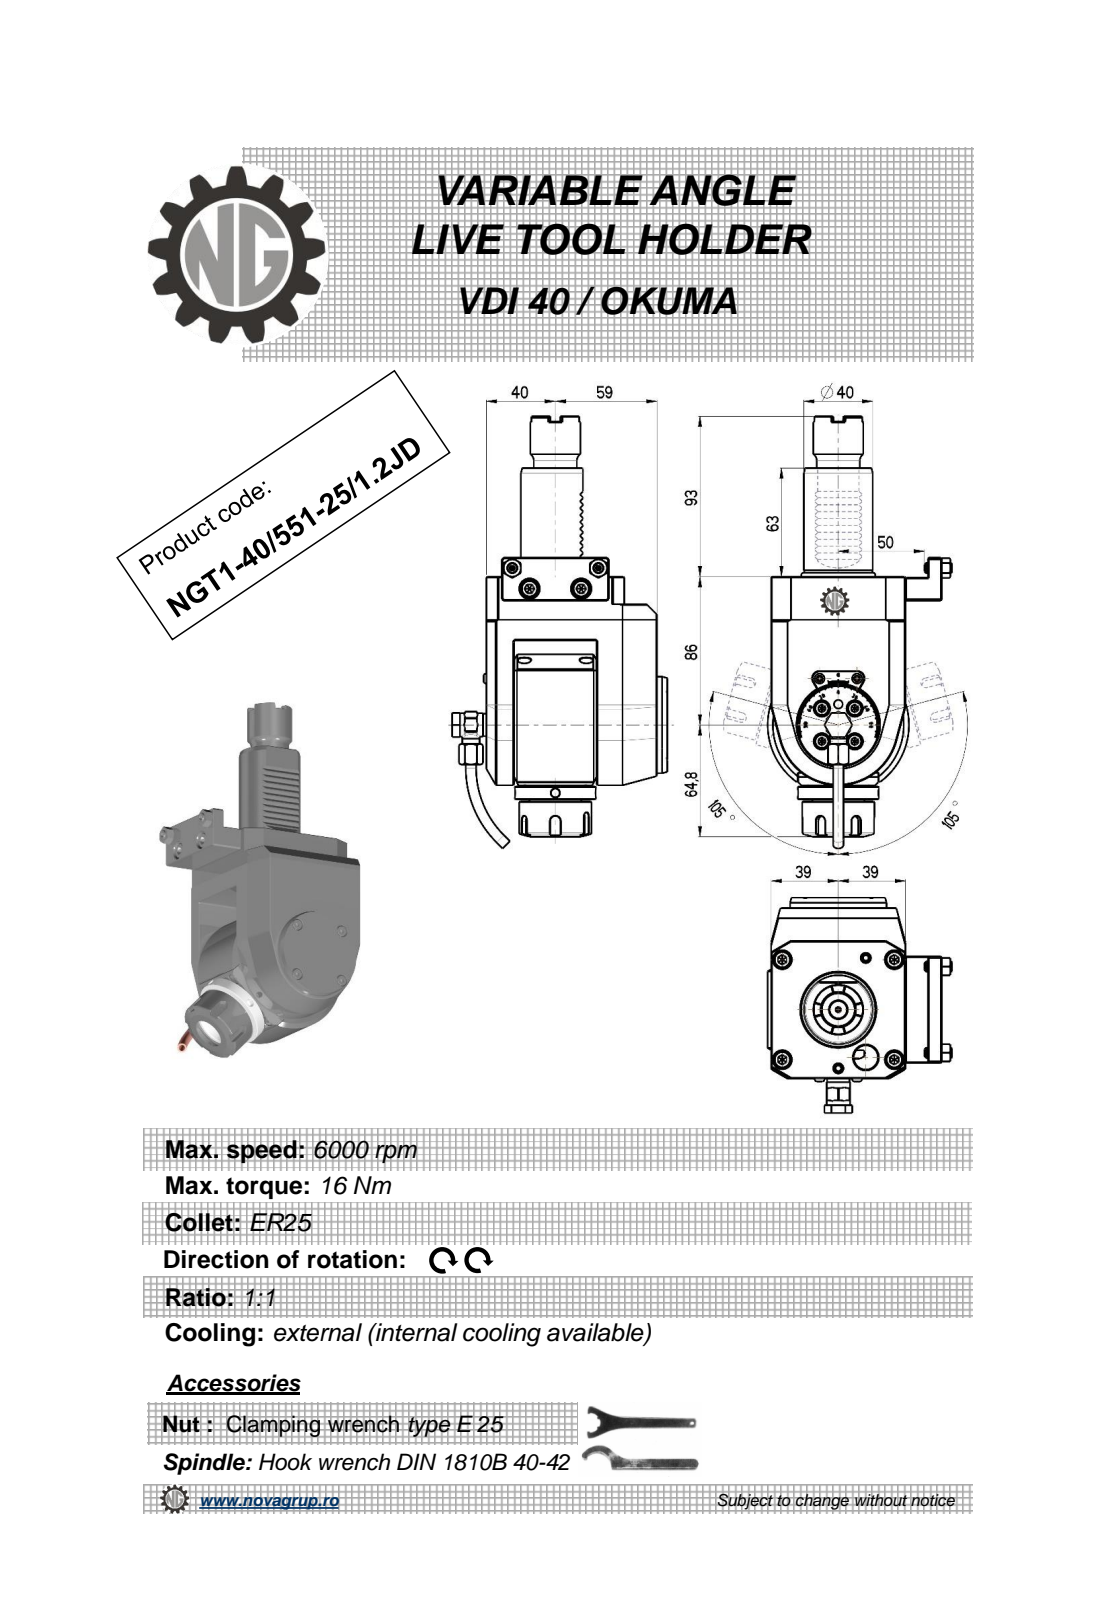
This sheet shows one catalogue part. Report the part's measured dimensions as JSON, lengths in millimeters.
{"part_name": "NGT1_40_551_25_1_2JD", "step_written_by": "PRO/ENGINEER BY PARAMETRIC TECHNOLOGY CORPORATION, 2010280 (CONFIG_CONTROL_DESIGN)", "units": "millimeters", "bodies": {"solids": 1, "faces": 599, "planar": 238, "cylindrical": 126, "other": 235}, "overall_size": [250.67, 124.9, 107], "volume_mm3": 950638, "surface_area_mm2": 88418, "round_holes": [[4, 3], [5, 2], [3, 1], [6.2, 1], [9, 1], [10, 1], [11, 1], [20.3, 1]], "round_bosses_or_shafts": [[6, 4], [5.7, 2], [82, 1], [56, 1], [47, 1], [42, 1], [40, 1], [35, 1]], "partial_cylinders_radius": [[0.3, 10], [0.31, 10], [3, 5], [0.5, 4], [10, 3], [1, 2], [7.7, 1], [35, 1]], "face_to_face_distances": [99, 16, 37, 78, 64, 21, 6, 105, 48, 8], "hole_center_spacings": [0.4, 39.45, 49, 49.4]}
